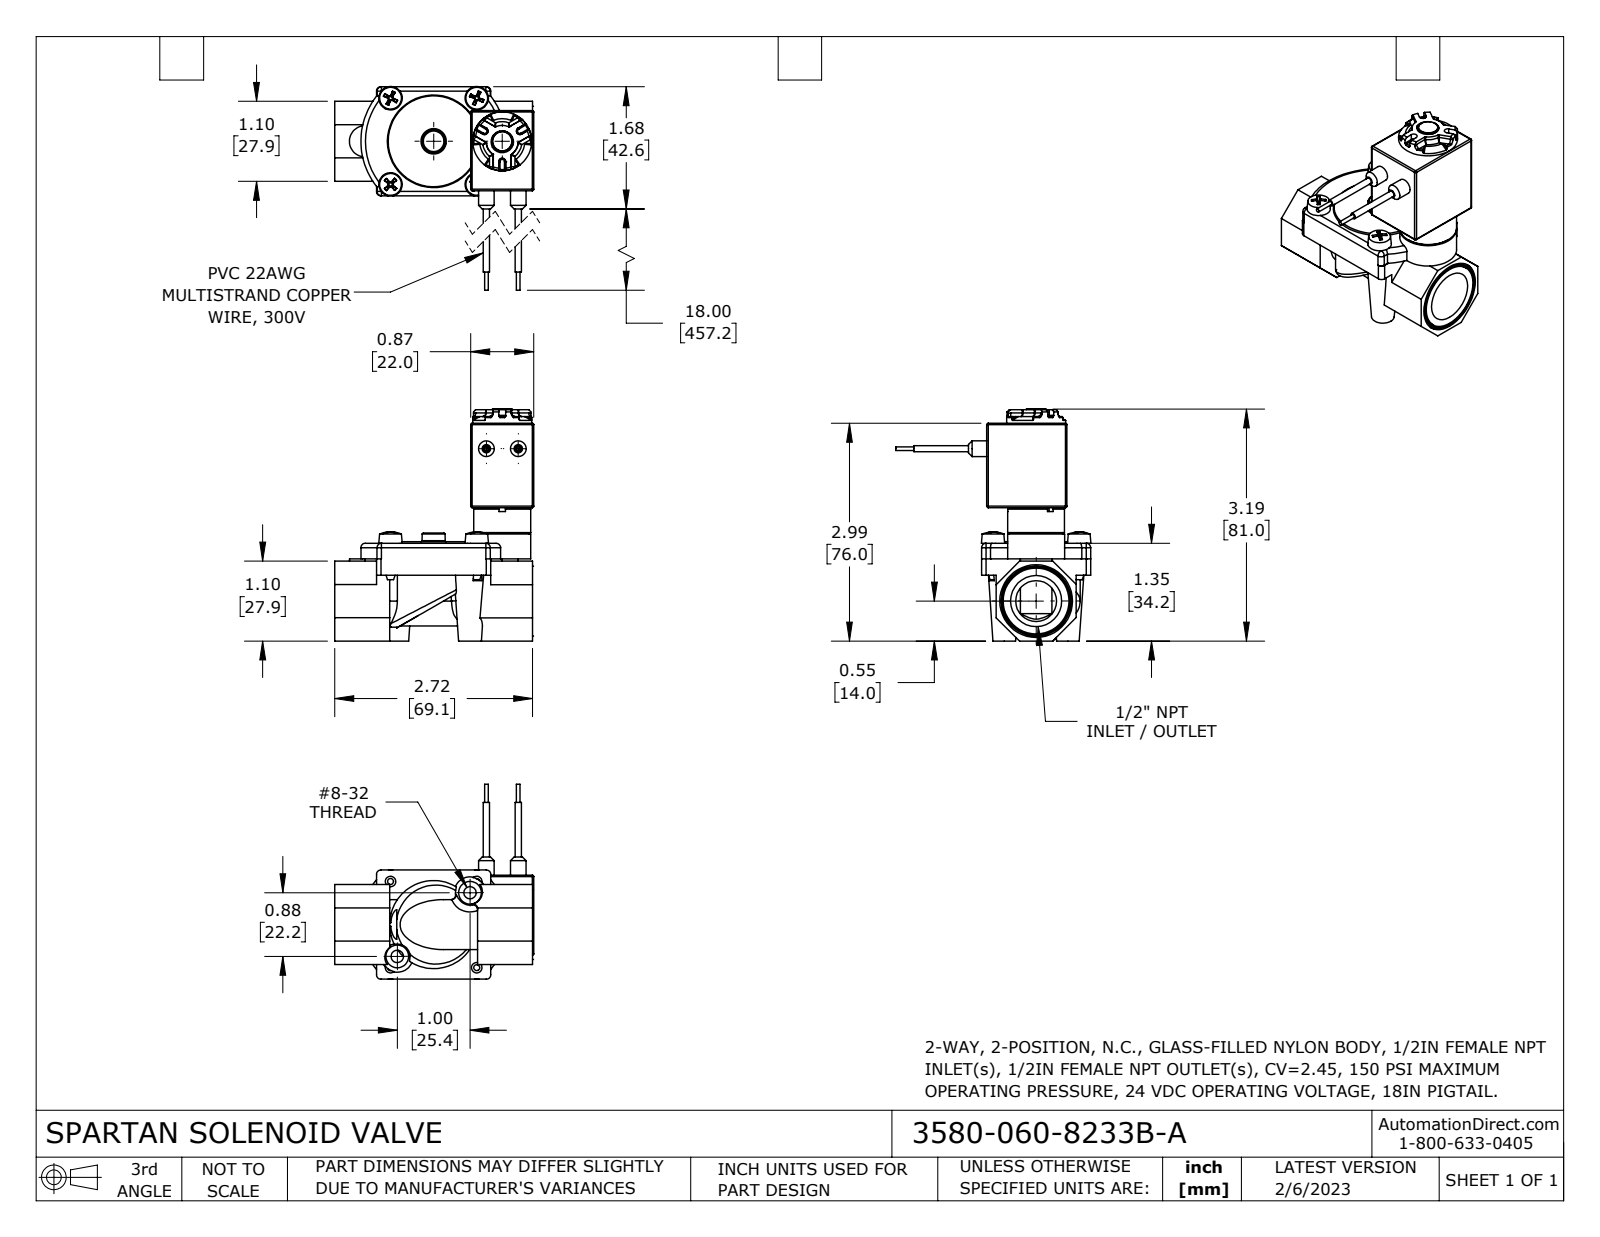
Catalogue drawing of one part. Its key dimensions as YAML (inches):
part_name: "3580-060-8233B-A"
step_written_by: "SolidWorks 2021 (CONFIG_CONTROL_DESIGN)"
units: inches
bodies: {solids: 1, faces: 627, planar: 197, cylindrical: 171, other: 259}
overall_size: [3.189, 2.736, 2.683]
volume: 3.419
surface_area: 42.98
round_holes:
  - {diameter: 0.144, count: 4}
  - {diameter: 0.093, count: 2}
  - {diameter: 0.17, count: 2}
  - {diameter: 0.36, count: 2}
  - {diameter: 0.703, count: 2}
  - {diameter: 0.062, count: 1}
  - {diameter: 0.156, count: 1}
  - {diameter: 0.268, count: 1}
  - {diameter: 0.285, count: 1}
  - {diameter: 0.312, count: 1}
  - {diameter: 0.315, count: 1}
  - {diameter: 0.321, count: 1}
round_bosses_or_shafts:
  - {diameter: 0.125, count: 4}
  - {diameter: 0.215, count: 2}
  - {diameter: 0.085, count: 2}
  - {diameter: 0.05, count: 2}
  - {diameter: 1.375, count: 1}
  - {diameter: 0.905, count: 1}
  - {diameter: 0.782, count: 1}
  - {diameter: 0.781, count: 1}
partial_cylinders:
  - {radius: 0.02, count: 12}
  - {radius: 0.062, count: 12}
  - {radius: 0.015, count: 6}
  - {radius: 0.05, count: 6}
  - {radius: 0.044, count: 3}
  - {radius: 0.215, count: 2}
  - {radius: 0.285, count: 1}
  - {radius: 0.314, count: 1}
face_to_face_distances: [1.1, 0.866, 0.2, 1.3, 0.02, 1.102, 1.365, 0.129, 0.127, 0.973]
hole_center_spacings: [0.838, 1.185, 0.181, 0.664, 0.688, 0.943, 1.034, 1.104]
